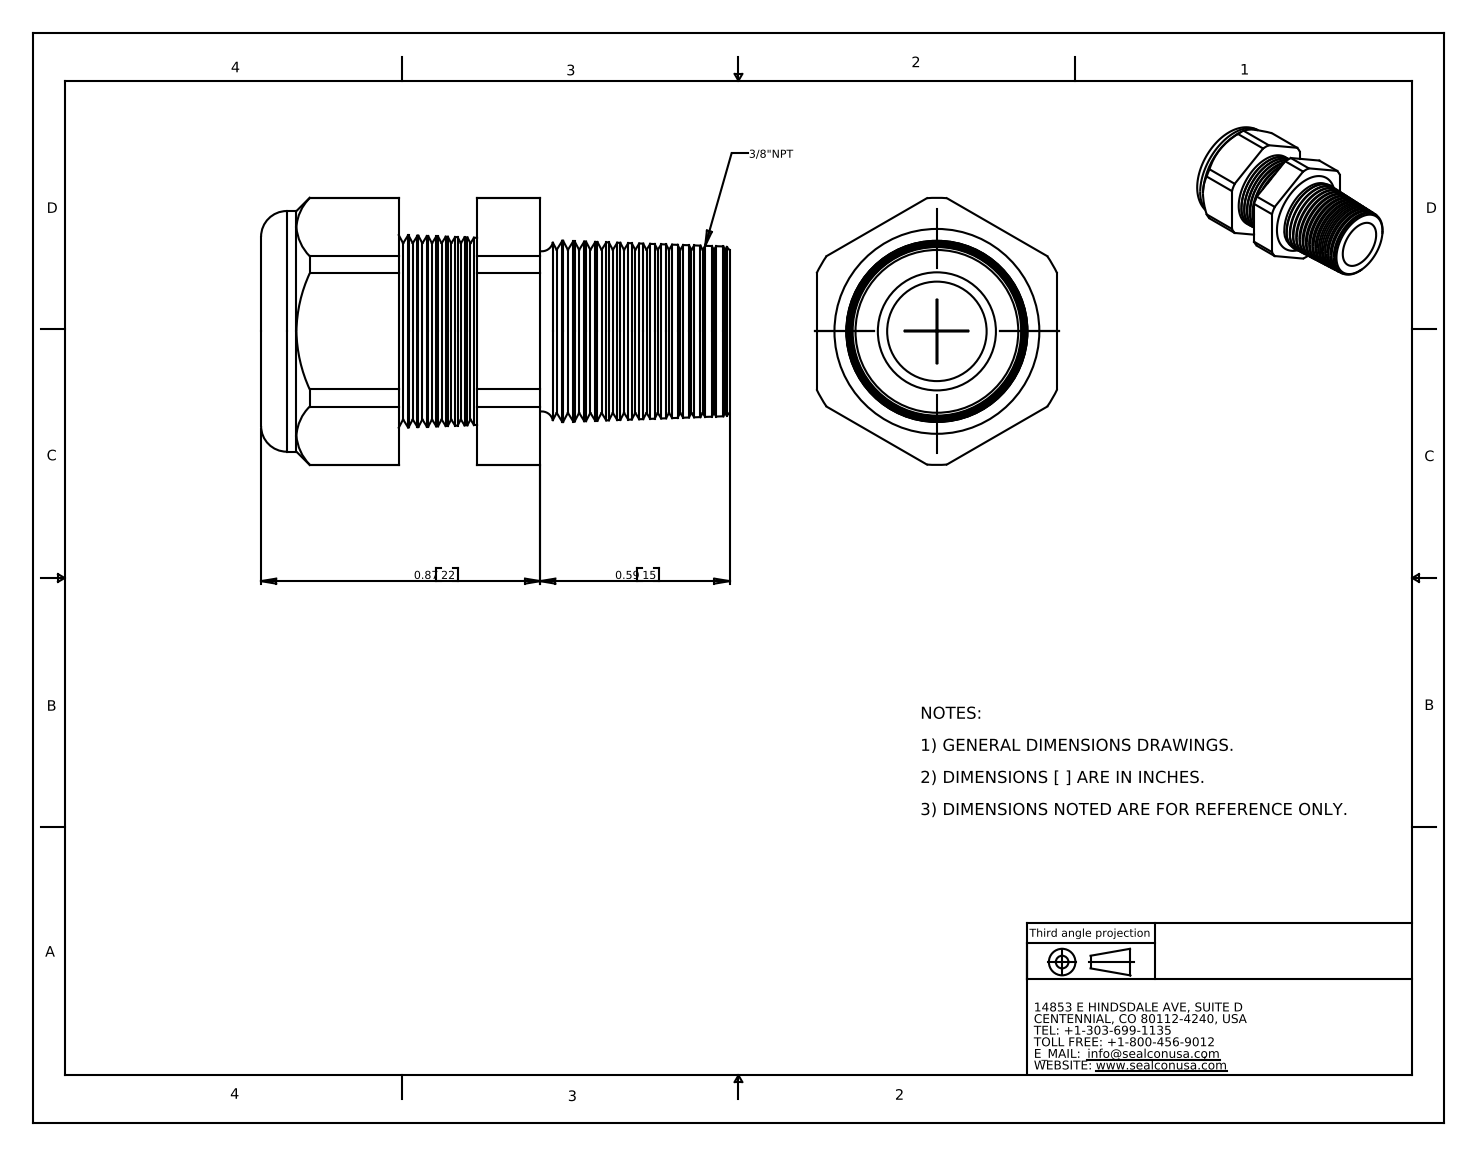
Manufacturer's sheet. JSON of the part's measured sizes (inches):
{"part_name": "CD09NP-GY", "step_written_by": "SolidWorks 2007 (CONFIG_CONTROL_DESIGN)", "units": "inches", "bodies": {"solids": 2, "faces": 198, "planar": 20, "cylindrical": 20, "other": 158}, "overall_size": [1.46, 0.833, 0.75], "volume_in3": 0.37, "surface_area_in2": 6.957, "round_holes": [[0.29, 1], [0.31, 1]], "round_bosses_or_shafts": [[0.75, 1]], "partial_cylinders_radius": [[0.416, 1]], "face_to_face_distances": [0.75, 0.673, 0.429, 0.244, 0.75, 0.87, 0.441, 0.197, 1.46, 1.031]}
